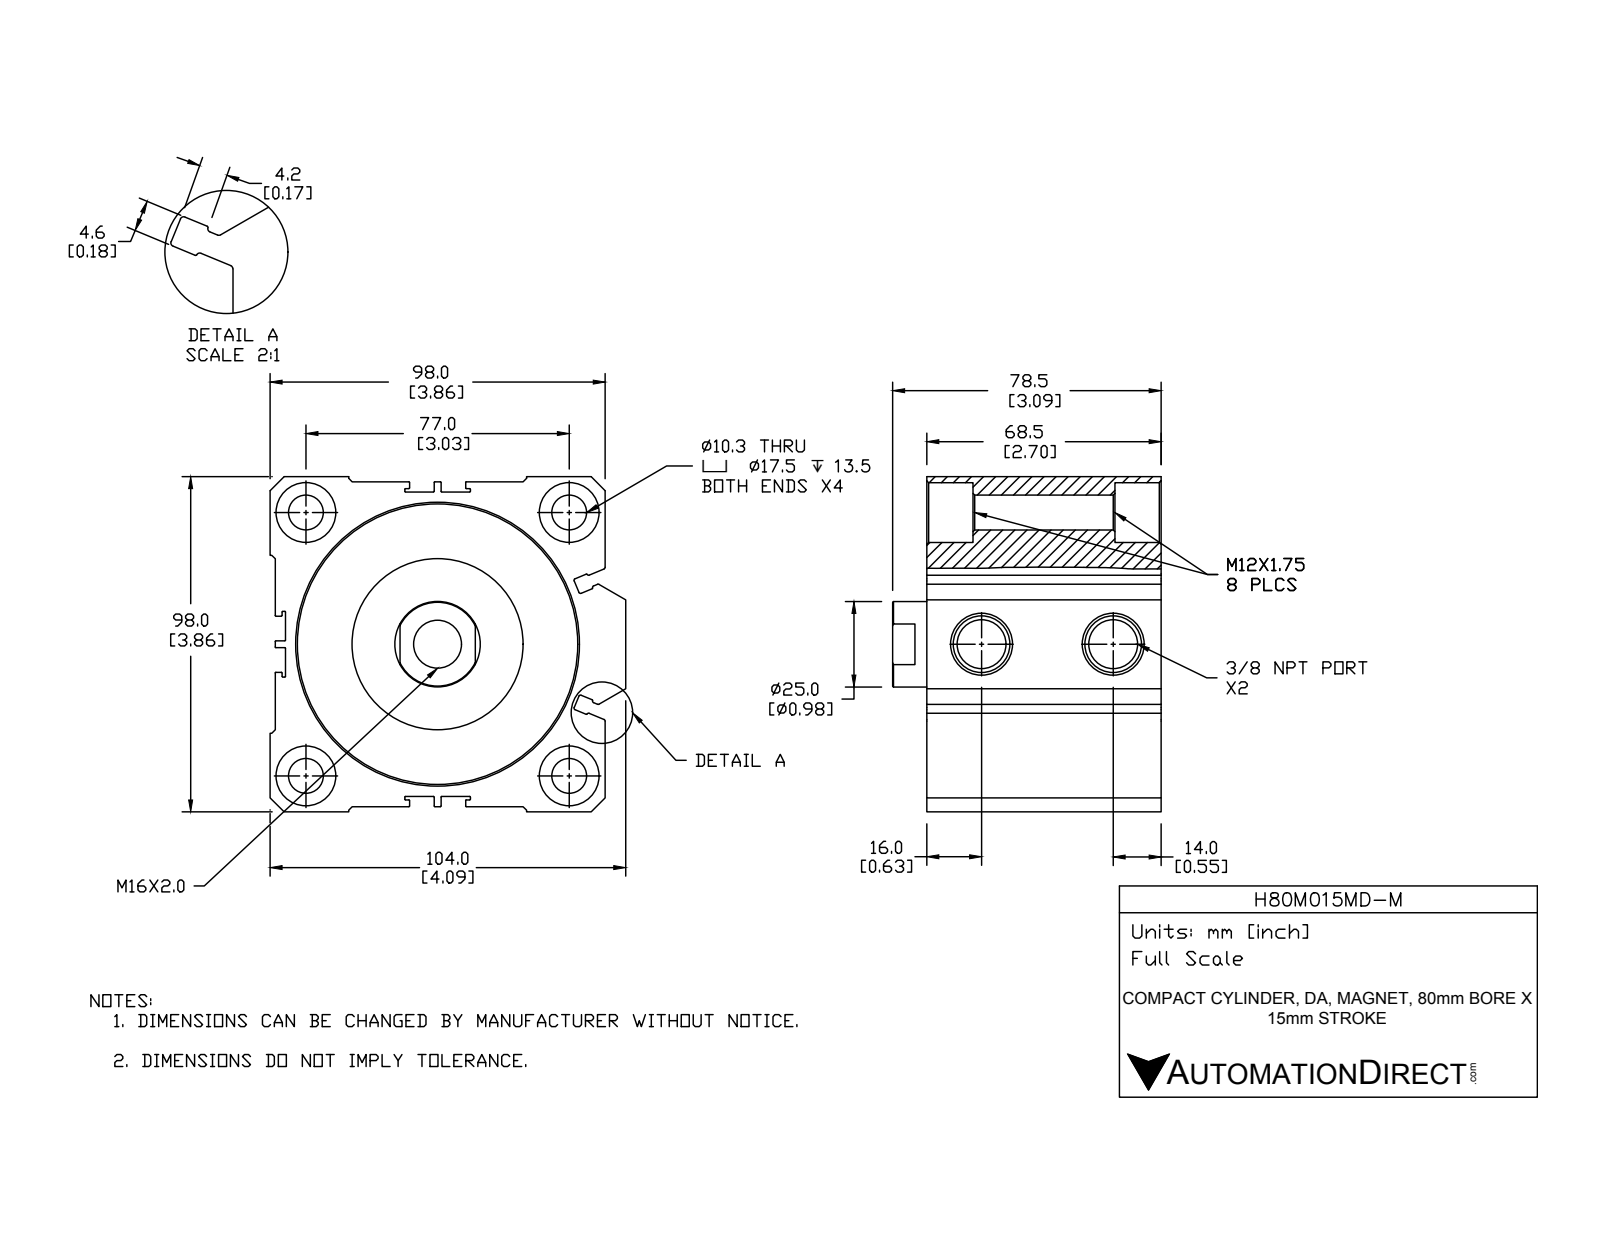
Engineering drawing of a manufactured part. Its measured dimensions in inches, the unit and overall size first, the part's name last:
Units: inches
Overall size (bounding box): 4.094 × 3.858 × 3.091
Round holes (diameter × count): ⌀0.402 ×4, ⌀0.689 ×4, ⌀0.562 ×2, ⌀0.551 ×1, ⌀0.984 ×1, ⌀1.792 ×1, ⌀3.15 ×1, ⌀3.228 ×1
Round bosses / shafts (diameter × count): ⌀1.969 ×1, ⌀1.535 ×1
Partial cylindrical surfaces — rounded edges, fillets, slot ends (radius × count): R0.008 ×40, R0.02 ×12
Main face-to-face distances: 0.059, 3.799, 3.858, 0.354, 0.591, 1.421, 1.067, 2.012, 1.657, 0.079
Hole centre spacings: 2.144, 3.031, 4.287, 1.516
Volume: 30.1 in³ · Surface area: 167.6 in²
Bodies: 2 solids, 261 faces (105 planar, 103 cylindrical, 53 other)
Part name (STEP PRODUCT): H80M015MD-M-PISTON; H80M015MD-M; H80M015MD-M-BODY
STEP written by: SolidWorks 2015 (CONFIG_CONTROL_DESIGN)
